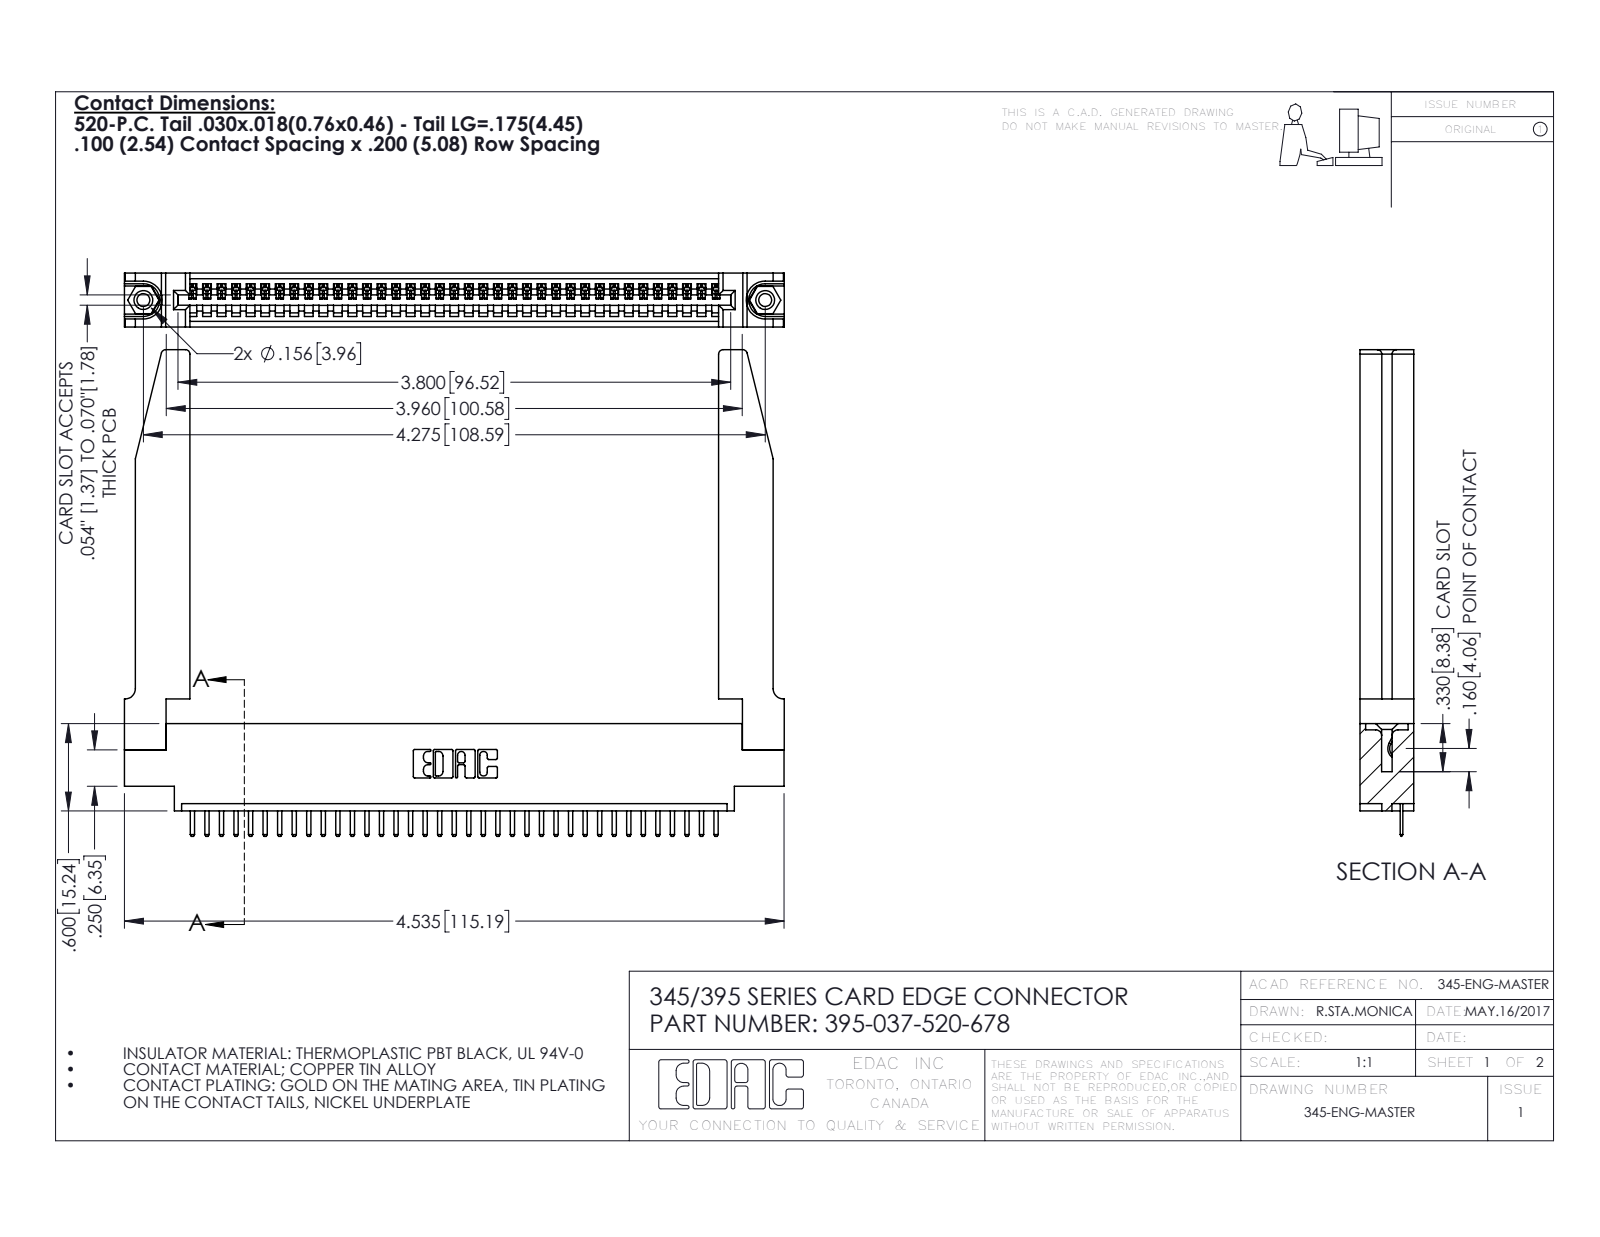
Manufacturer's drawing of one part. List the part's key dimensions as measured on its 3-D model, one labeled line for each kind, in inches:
Part name (STEP PRODUCT): 345 Part_0.170 Offset - 0.156 Dia-TH; 345-220-078_345-220-078; 345-250-001_345-250-001-102; 395-037-520-678 (+1 more)
STEP written by: SolidWorks 2016 (CONFIG_CONTROL_DESIGN)
Units: inches
Bodies: 42 solids, 2658 faces (1780 planar, 826 cylindrical, 52 other)
Overall size (bounding box): 4.536 × 3.345 × 0.37
Volume: 1.126 in³ · Surface area: 32.17 in²
Round holes (diameter × count): ⌀0.089 ×2, ⌀0.125 ×2, ⌀0.156 ×2, ⌀0.064 ×1
Round bosses / shafts (diameter × count): ⌀0.155 ×2
Partial cylindrical surfaces — rounded edges, fillets, slot ends (radius × count): R0.01 ×76, R0.006 ×74, R0.01 ×22, R0.03 ×8, R0.007 ×6, R0.031 ×6, R0.026 ×3, R0.031 ×2
Main face-to-face distances: 0.37, 0.072, 0.298, 0.098, 0.272, 0.025, 0.2, 0.225, 0.15, 0.148
Hole centre spacings: 0.27, 4.039, 4.275
